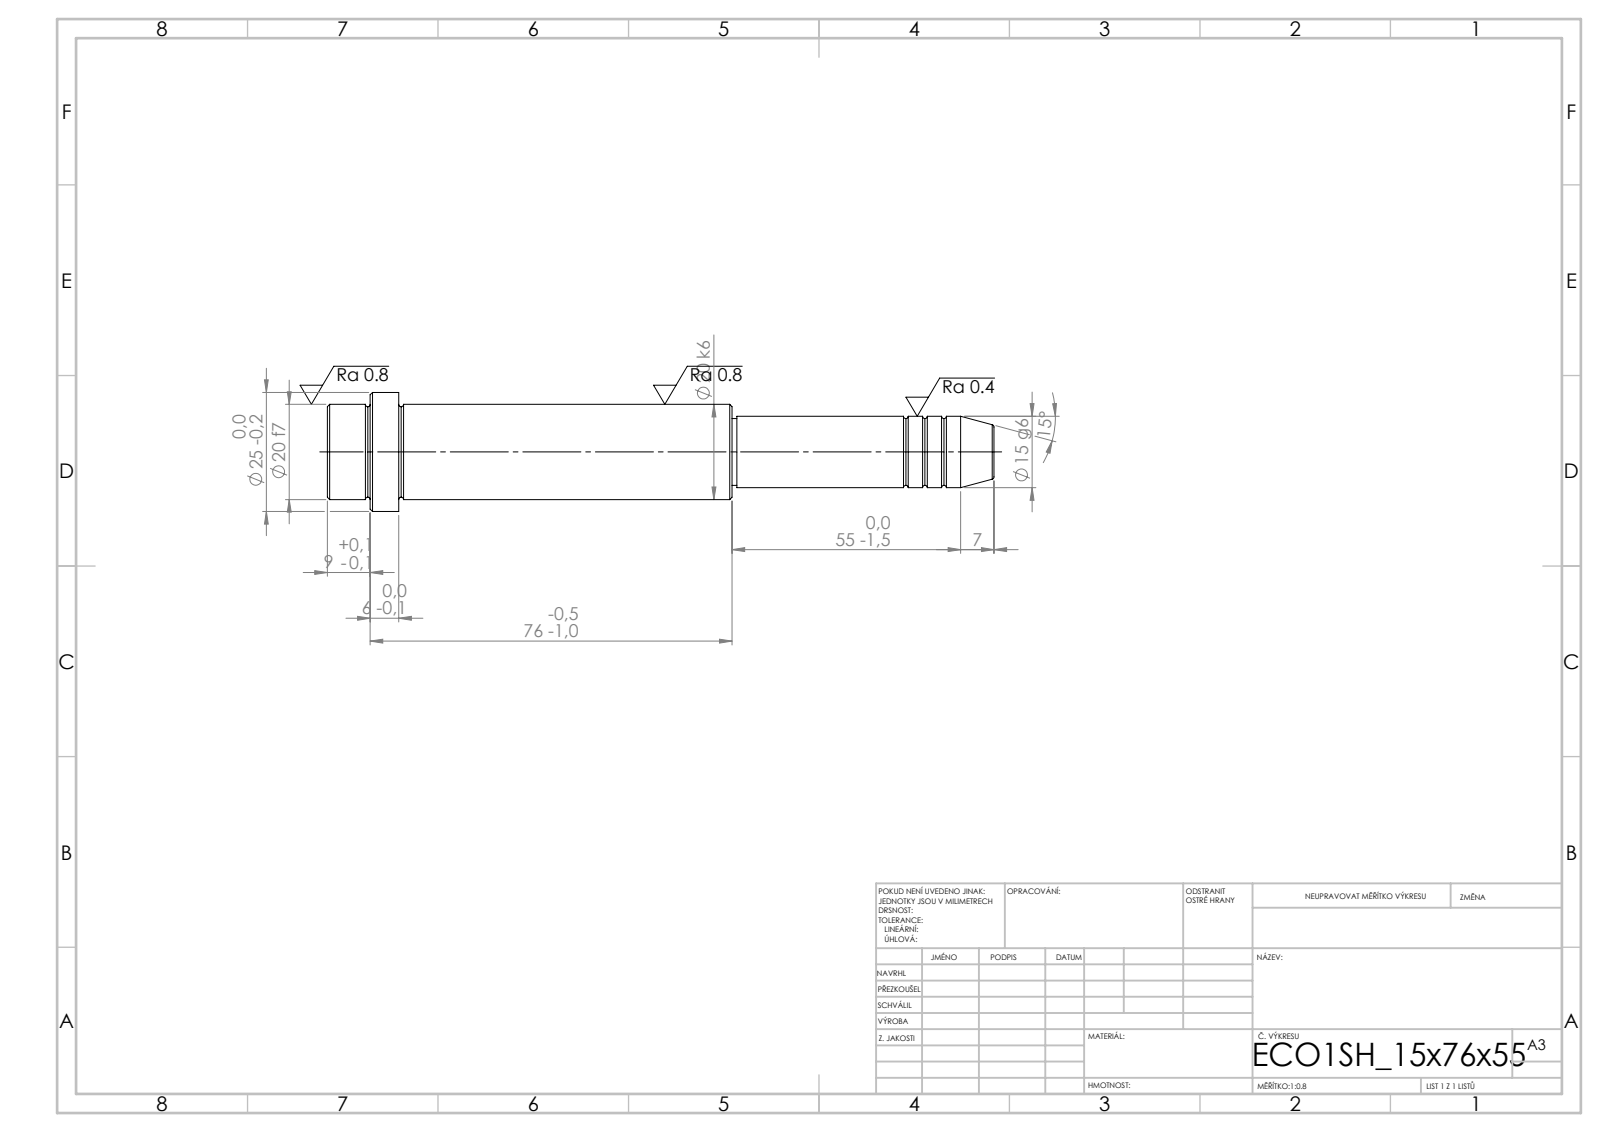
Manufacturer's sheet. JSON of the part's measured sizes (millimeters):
{"step_written_by": "SolidWorks 2019 (CONFIG_CONTROL_DESIGN)", "units": "millimeters", "bodies": {"solids": 1, "faces": 52, "planar": 6, "cylindrical": 16, "other": 30}, "overall_size": [140, 25, 25], "volume_mm3": 37048, "surface_area_mm2": 9014, "round_bosses_or_shafts": [[25, 1], [20, 1], [15, 1], [14, 1]], "face_to_face_distances": [15, 6, 9, 70, 76, 85, 55, 125, 131, 140]}
